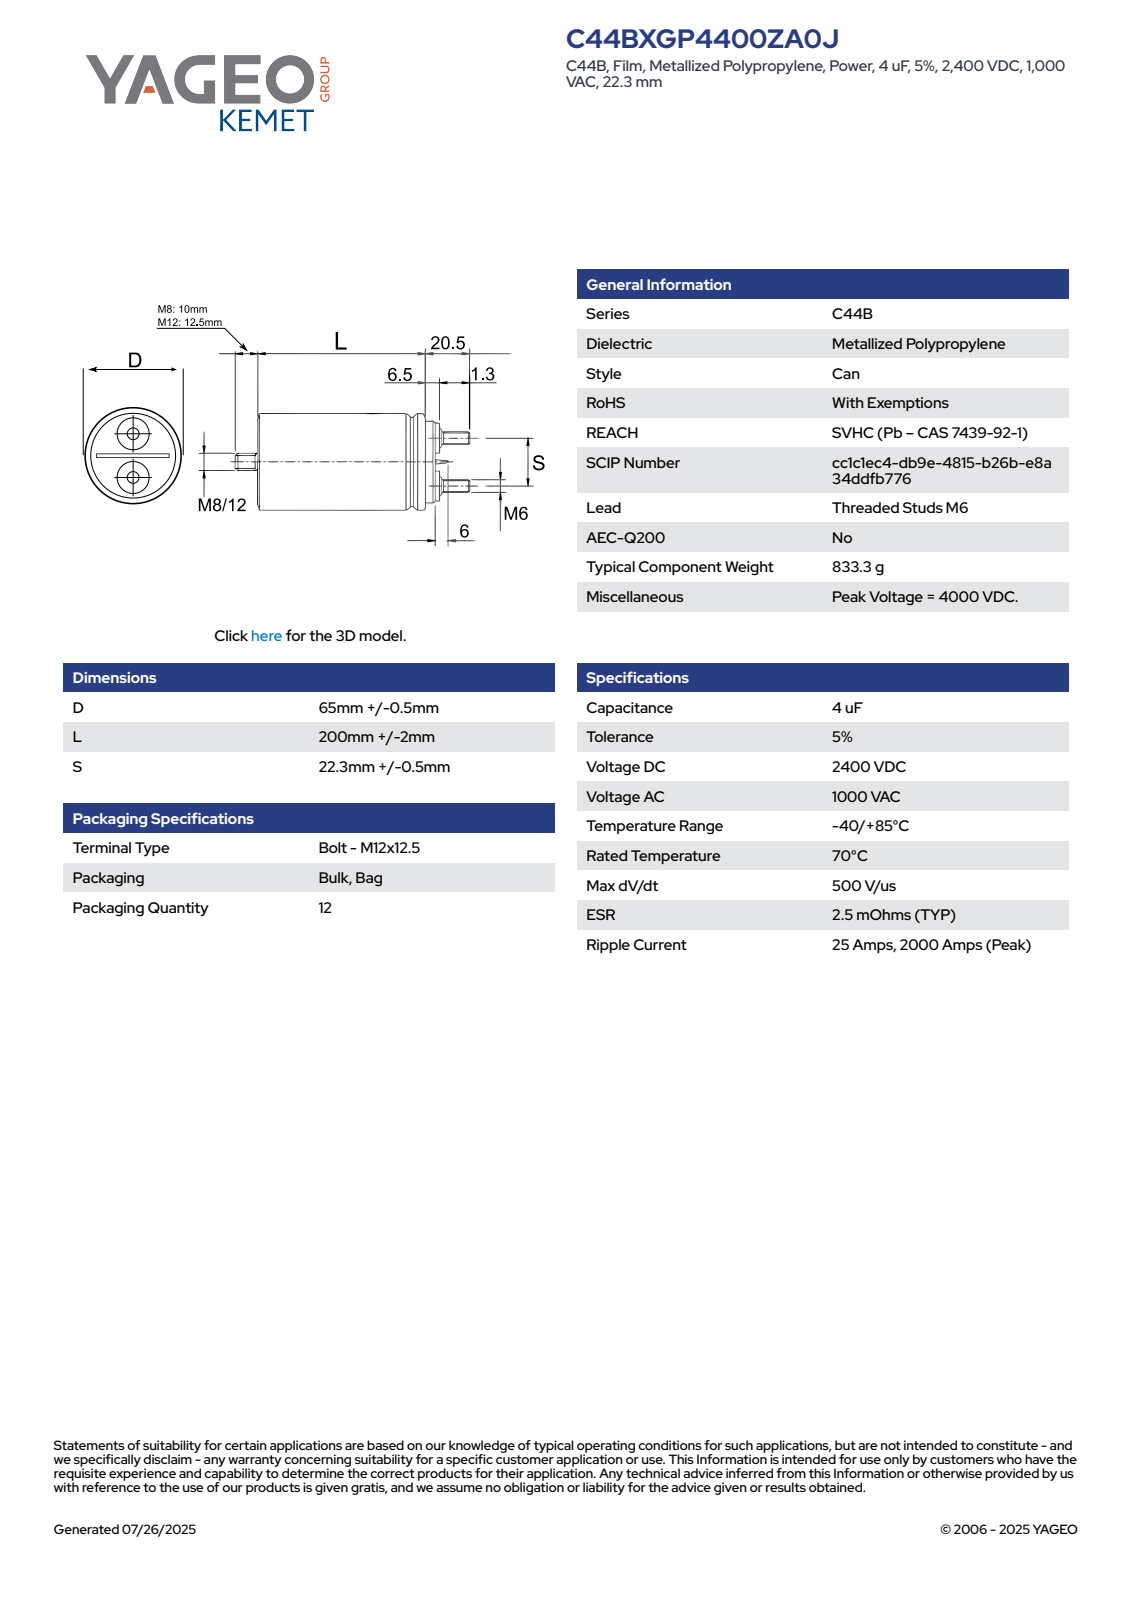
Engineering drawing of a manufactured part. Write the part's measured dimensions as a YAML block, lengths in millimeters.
part_name: "CFP_M6_65X200_D65.5L202S22.8"
step_written_by: "SolidWorks 2014 (AUTOMOTIVE_DESIGN)"
units: millimeters
bodies: {solids: 1, faces: 117, planar: 35, cylindrical: 39, other: 43}
overall_size: [234.5, 65.51, 65.5]
volume: 688151
surface_area: 51643
round_bosses_or_shafts:
  - {diameter: 18, count: 2}
  - {diameter: 13, count: 2}
  - {diameter: 6, count: 2}
  - {diameter: 65.5, count: 1}
  - {diameter: 57.97, count: 1}
  - {diameter: 12, count: 1}
partial_cylinders:
  - {radius: 0.35, count: 1}
  - {radius: 32.76, count: 1}
face_to_face_distances: [206, 202, 4, 0.7, 208.5, 6.5, 2.5, 209.5, 7.5, 3.5]
